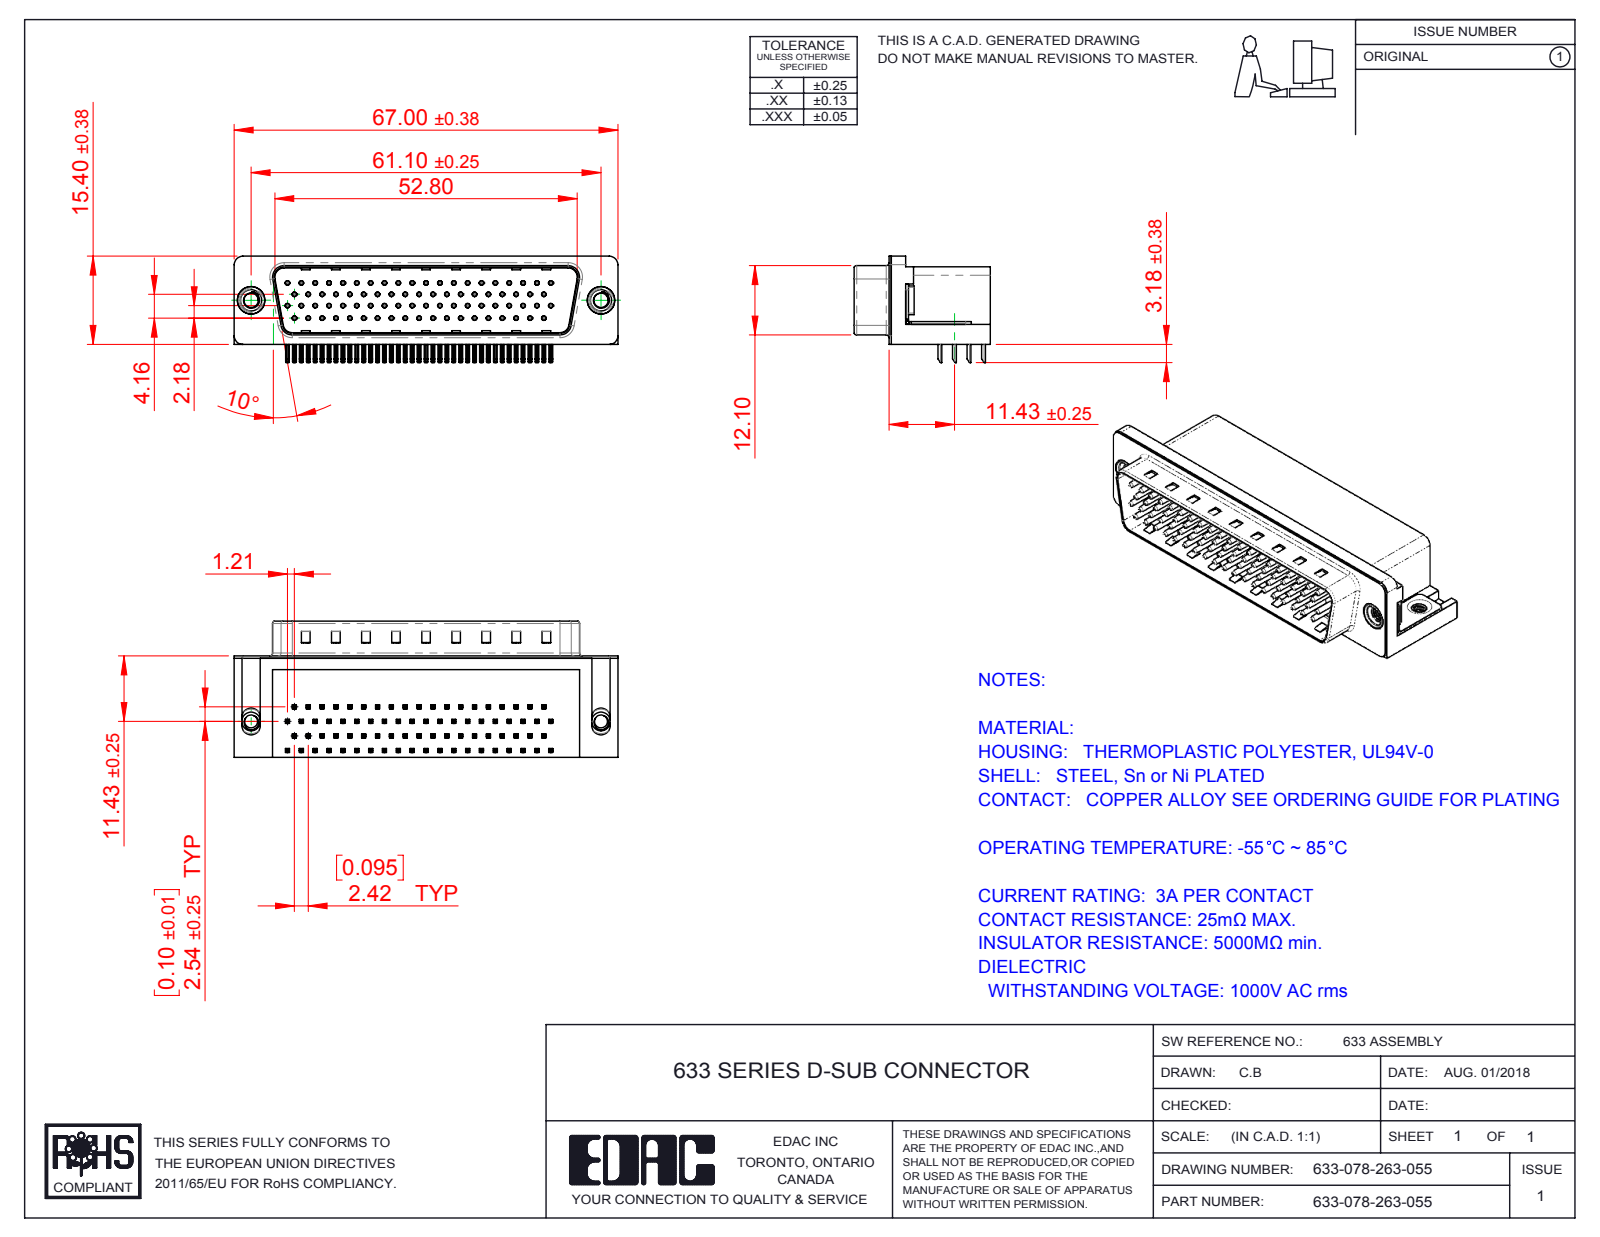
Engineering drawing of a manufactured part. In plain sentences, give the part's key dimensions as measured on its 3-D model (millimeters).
The part is named "633 Shell_78 Contact; 633 Housing_78 Contact; 633 Contact Bottom_78 Contact; 633 M3 Threaded Rivet (+5 more)". Its 3-D file was written by "SolidWorks 2016 (CONFIG_CONTROL_DESIGN)". It is 84 solids with 6306 faces: 3981 planar, 1794 cylindrical and 531 other. Overall it measures 67 by 23.8 by 18.58 millimeters. Its volume is 14 619 cubic millimeters and its surface area 16 431 square millimeters. Round holes: 78 of diameter 0.35, 78 of diameter 0.8, 2 of diameter 2.26, 2 of diameter 2.5, 2 of diameter 4, 2 of diameter 4.8, 2 of diameter 5. Round bosses or shafts: 78 of diameter 0.75, 2 of diameter 4.9, 2 of diameter 4.75, 2 of diameter 3.9, 2 of diameter 3.26. Partial cylindrical surfaces (rounded edges, fillets, slot ends): 320 of radius 0.25, 156 of radius 0.12, 16 of radius 1, 9 of radius 0.5, 8 of radius 1.6, 6 of radius 1.5, 4 of radius 0.45, 4 of radius 0.9. The main face-to-face distances are 0.4, 13.2, 17.3, 11.7, 13.35, 2.05, 13.75, 1.65, 1.85, 11.9. The hole center spacings are 2.42, 4.84, 7.26, 9.68, 6.26, 7.13, 12.1, 8.62.
